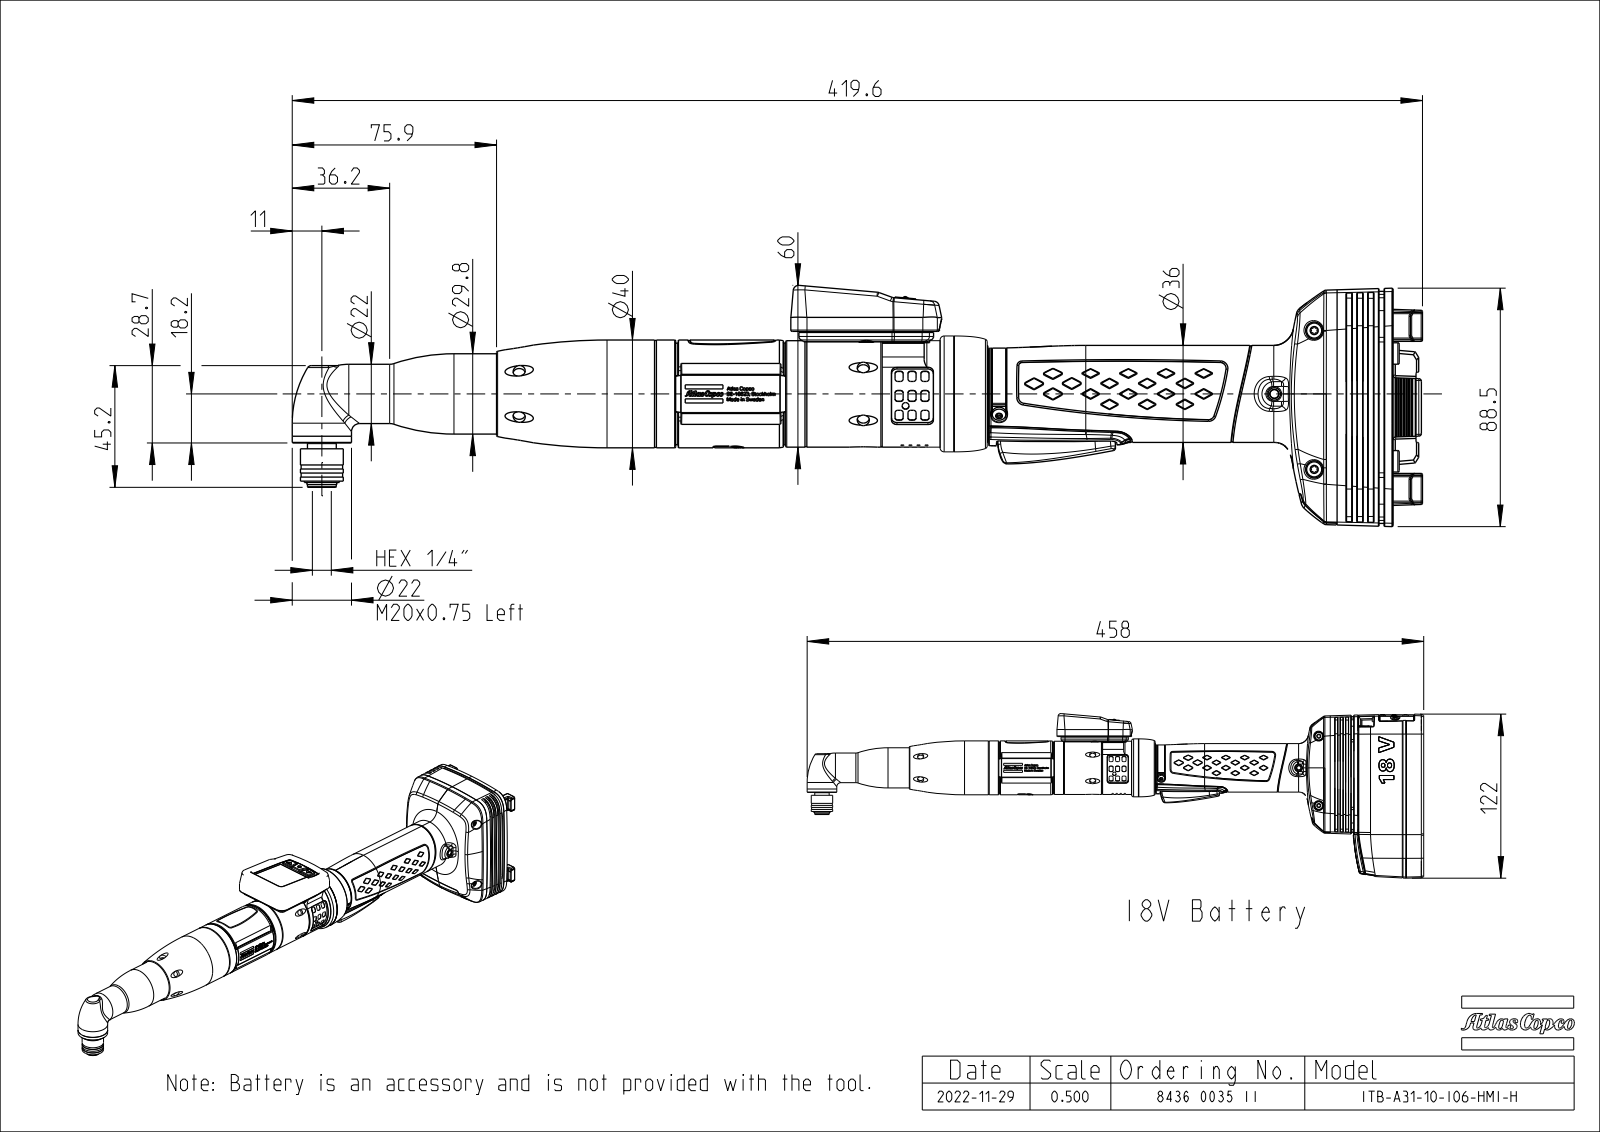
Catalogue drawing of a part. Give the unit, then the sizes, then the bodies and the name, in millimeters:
Units: millimetres
Overall size (bounding box): 420.1 × 89.5 × 74.5
Round holes (diameter × count): ⌀1 ×12, ⌀3.2 ×11, ⌀2.5 ×9, ⌀4.5 ×7, ⌀3 ×6, ⌀2.6 ×5, ⌀2.2 ×4, ⌀3.3 ×4, ⌀4.3 ×4, ⌀5.8 ×4, ⌀6.5 ×4, ⌀4 ×3
Round bosses / shafts (diameter × count): ⌀6.2 ×4, ⌀5.5 ×4, ⌀4 ×4, ⌀5 ×3, ⌀3.5 ×3, ⌀22 ×2, ⌀5.6 ×2, ⌀3 ×2
Partial cylindrical surfaces — rounded edges, fillets, slot ends (radius × count): R0.3 ×447, R0.5 ×241, R0.2 ×231, R0.4 ×122, R1 ×118, R2 ×106, R0.1 ×42, R3 ×29
Main face-to-face distances: 11.2, 2, 3, 20.2, 9, 34.2, 2.2, 13.5, 22.7, 22.9
Hole centre spacings: 3, 6, 8.8, 12.4, 19.1, 55.5, 58.3, 78.2
Volume: 445 900 mm³ · Surface area: 180 600 mm²
Bodies: 9 solids, 12893 faces (4562 planar, 2696 cylindrical, 5635 other)
Part name (STEP PRODUCT): EXT_COMP_SW0024
STEP written by: CREO PARAMETRIC BY PTC INC, 2020281 (CONFIG_CONTROL_DESIGN)
